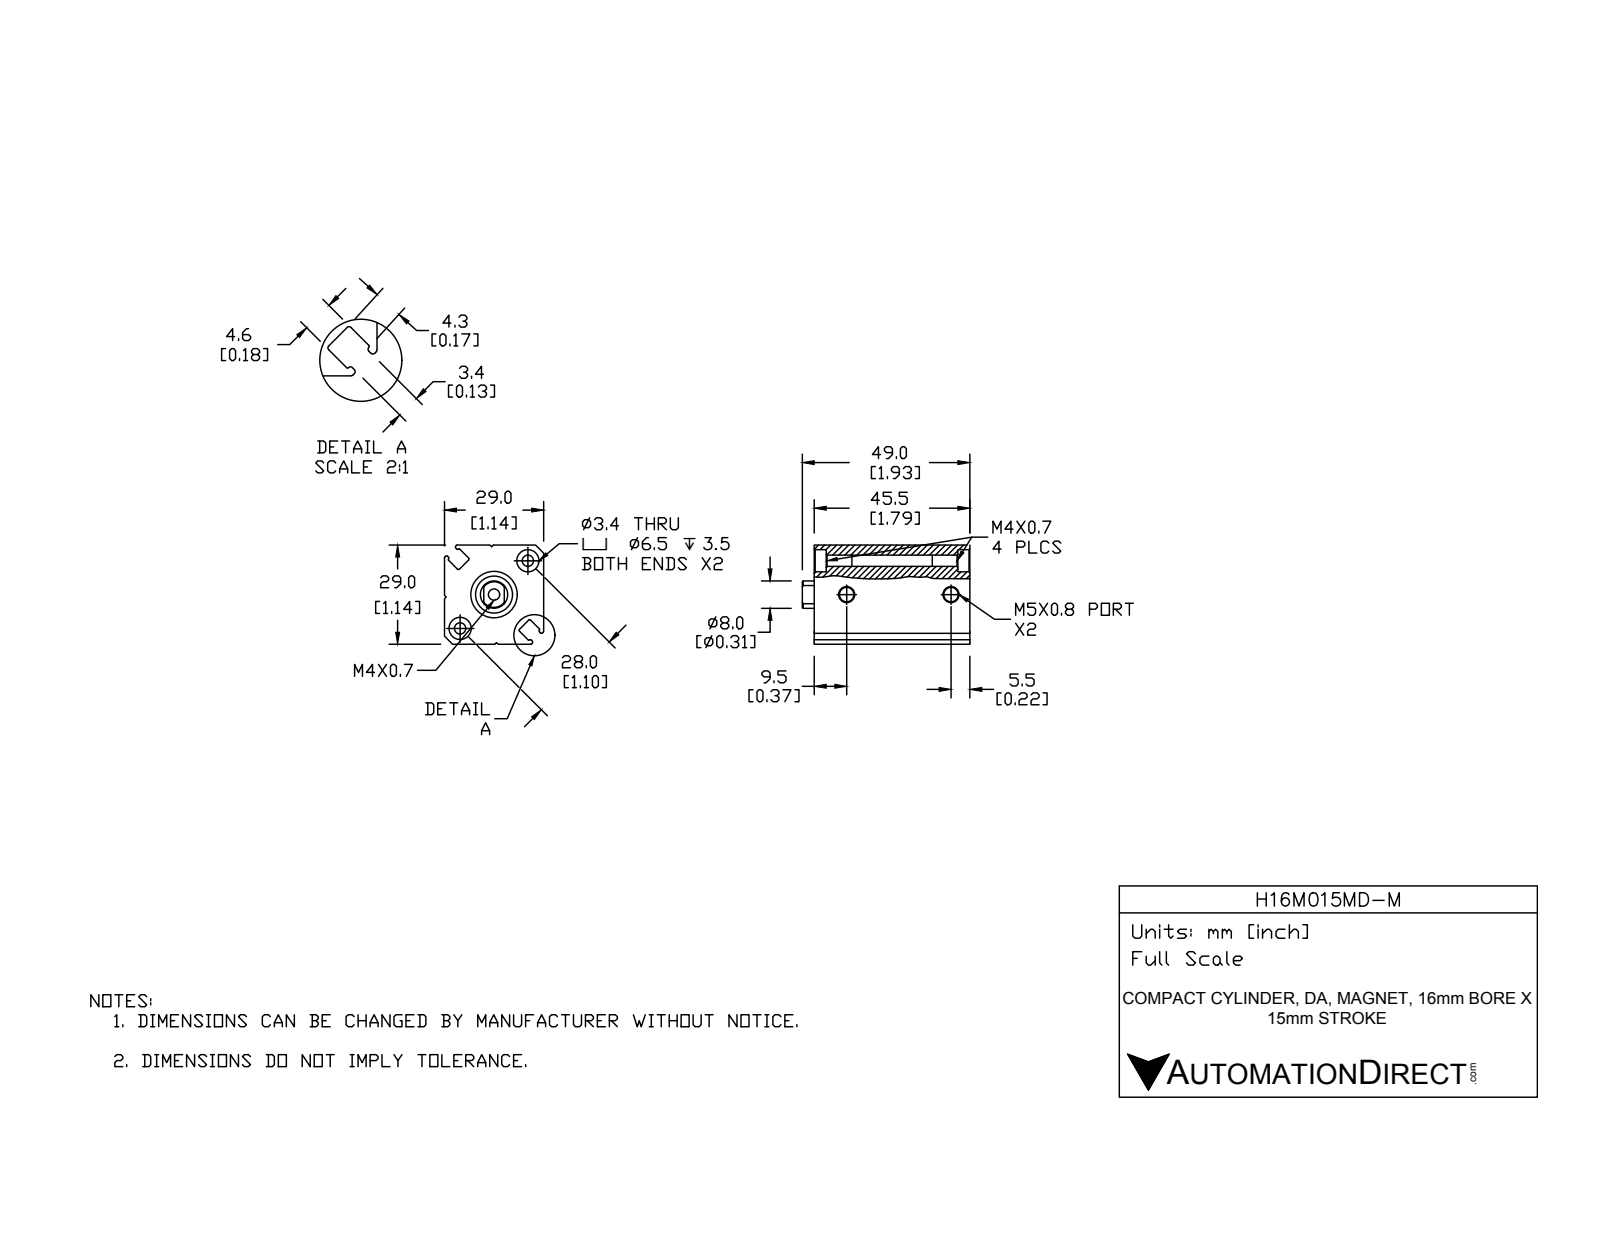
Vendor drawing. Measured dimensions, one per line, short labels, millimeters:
name: H16M015MD-M; H16M015MD-M-PISTON; H16M015MD-M-BODY
written by: SolidWorks 2015 (CONFIG_CONTROL_DESIGN)
unit: mm
bodies: 2 solids, 128 faces (49 planar, 54 cylindrical, 25 other)
size: 49 × 29 × 29
volume: 31 389 mm³; area: 13 173 mm²
holes: 3× ⌀3.3, 2× ⌀4.2, 2× ⌀6.5, 1× ⌀8, 1× ⌀13.6, 1× ⌀16
bosses: 1× ⌀10.8
rounds: 16× R0.4, 4× R0.2
face distances: 29, 45.5, 4, 41.5, 4.6, 16.53, 21.13, 24.84, 37.66, 20.2
hole spacings: 14, 28, 30.5
